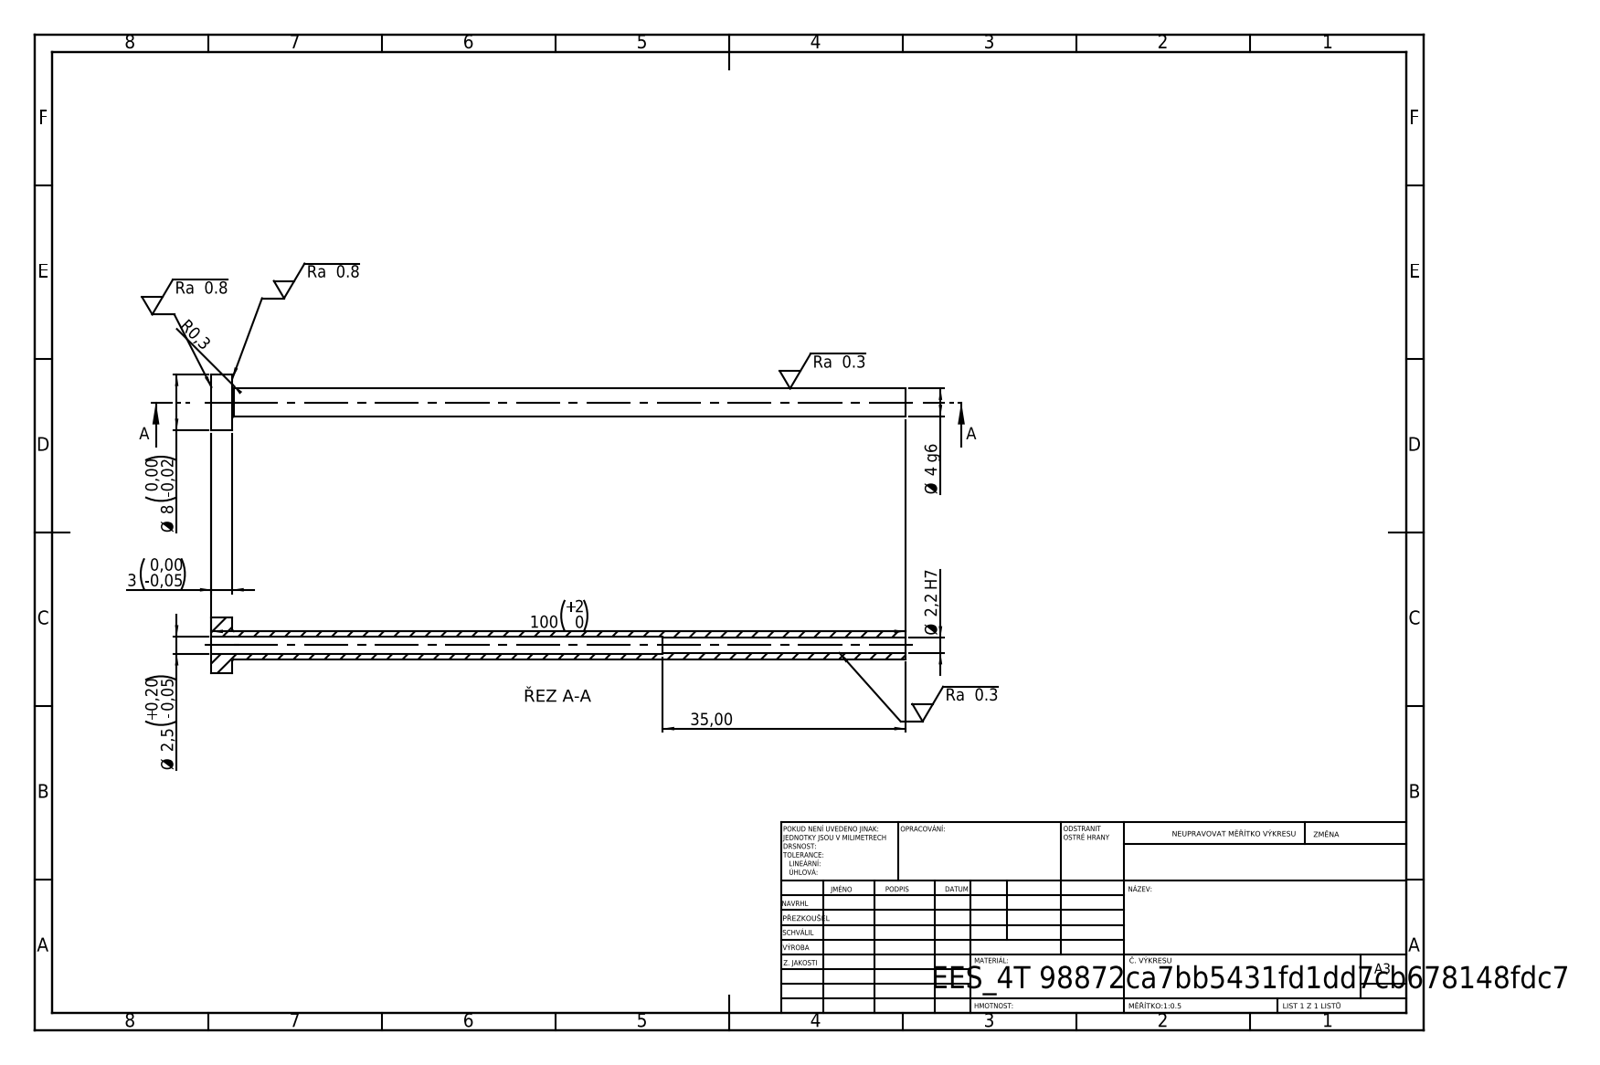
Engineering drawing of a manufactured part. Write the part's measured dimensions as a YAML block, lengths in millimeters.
step_written_by: "SolidWorks 2019 (CONFIG_CONTROL_DESIGN)"
units: millimeters
bodies: {solids: 1, faces: 14, planar: 4, cylindrical: 8, other: 2}
overall_size: [100, 8, 8]
volume: 918
surface_area: 2138
round_holes:
  - {diameter: 2.2, count: 1}
  - {diameter: 2.5, count: 1}
round_bosses_or_shafts:
  - {diameter: 8, count: 1}
  - {diameter: 4, count: 1}
face_to_face_distances: [3, 100, 97, 65, 62, 35]
